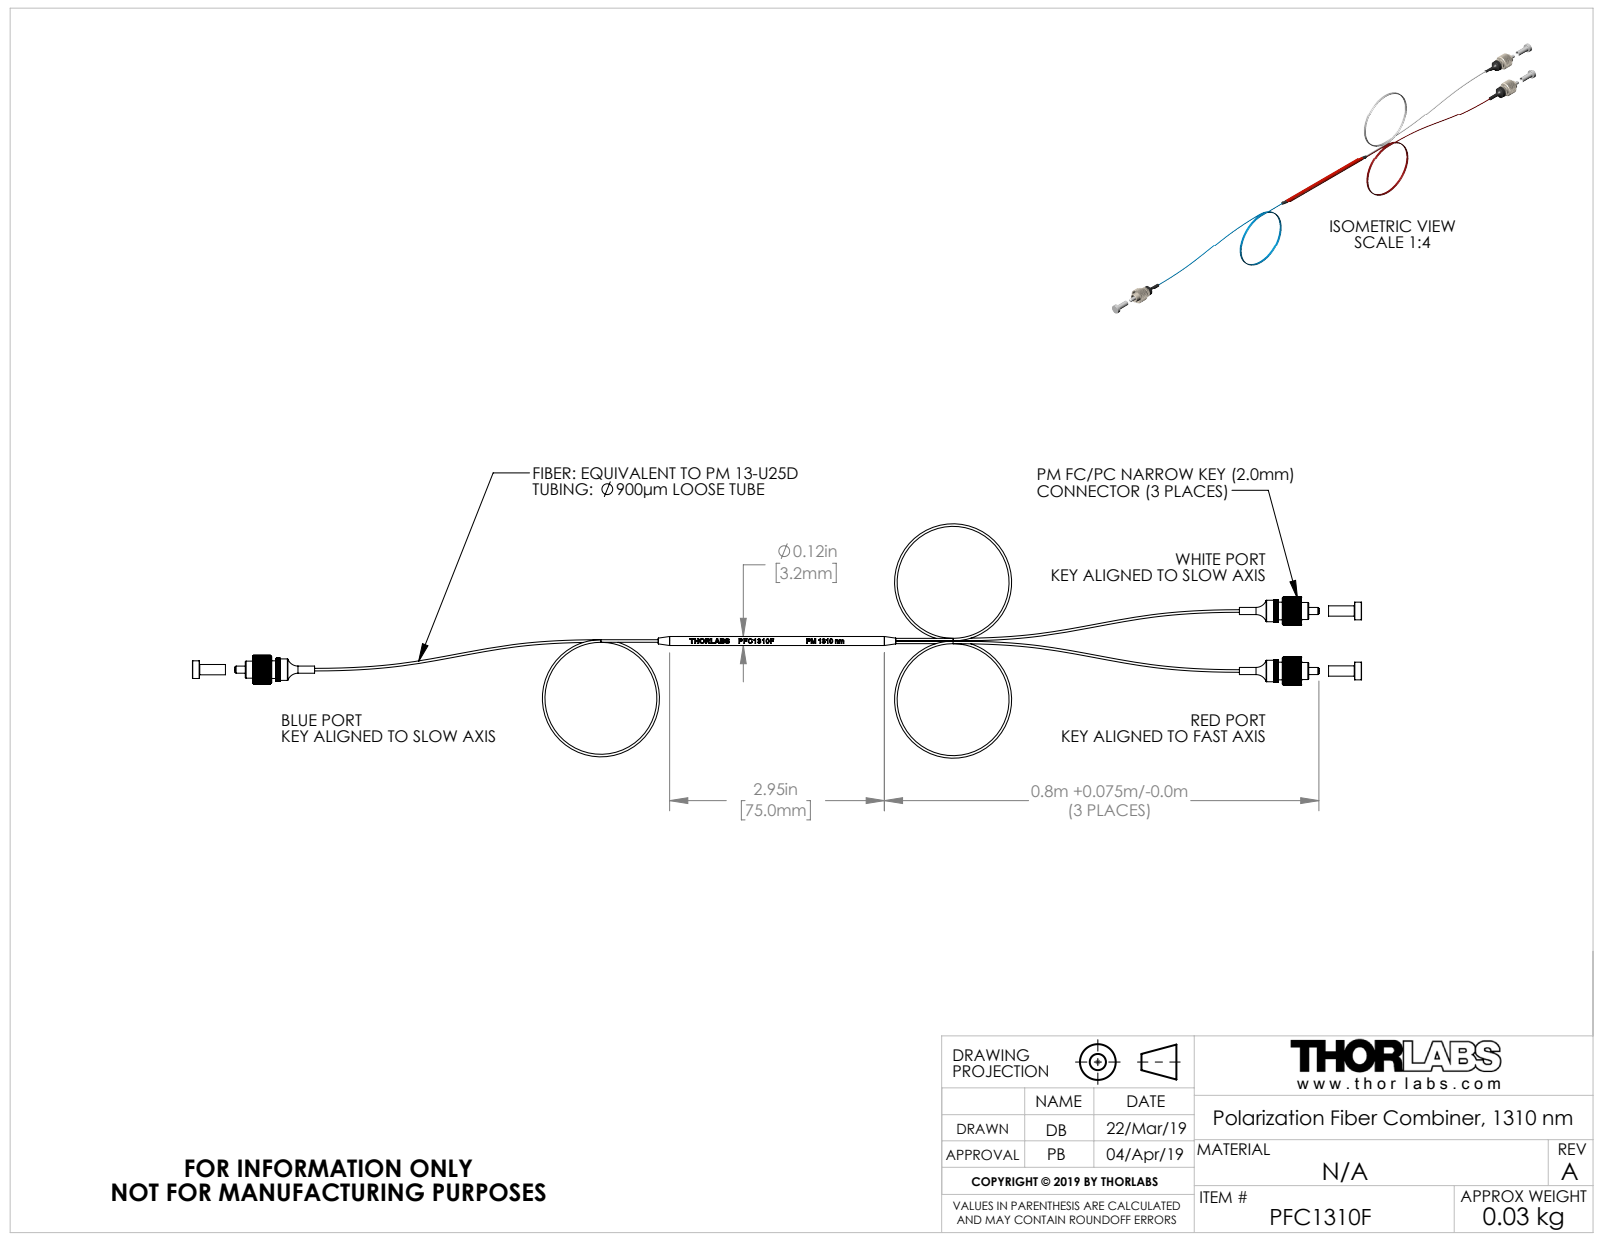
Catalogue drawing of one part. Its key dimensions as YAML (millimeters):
part_name: "DWG1751_48-2mm; PANDA 1310_60; DWG1631_75mm; DWG1528 (+8 more)"
step_written_by: "SolidWorks 2018 (CONFIG_CONTROL_DESIGN)"
units: millimeters
bodies: {solids: 32, faces: 2605, planar: 1271, cylindrical: 884, other: 450}
overall_size: [408.3, 81.85, 13.99]
volume: 3282
surface_area: 13603
round_holes:
  - {diameter: 0.5, count: 6}
  - {diameter: 0.9, count: 3}
  - {diameter: 0.95, count: 3}
  - {diameter: 1, count: 3}
  - {diameter: 2.5, count: 3}
  - {diameter: 2.8, count: 3}
  - {diameter: 3.36, count: 3}
  - {diameter: 4.38, count: 3}
  - {diameter: 4.4, count: 3}
  - {diameter: 5.08, count: 3}
  - {diameter: 5.55, count: 3}
  - {diameter: 6.1, count: 3}
round_bosses_or_shafts:
  - {diameter: 7.5, count: 3}
  - {diameter: 7.07, count: 3}
  - {diameter: 6.17, count: 3}
  - {diameter: 6.08, count: 3}
  - {diameter: 5.95, count: 3}
  - {diameter: 5.38, count: 3}
  - {diameter: 4.85, count: 3}
  - {diameter: 3.6, count: 3}
partial_cylinders:
  - {radius: 0.5, count: 6}
  - {radius: 0.75, count: 3}
  - {radius: 1.55, count: 3}
  - {radius: 2.26, count: 3}
  - {radius: 3.98, count: 3}
  - {radius: 5, count: 3}
  - {radius: 0.45, count: 2}
  - {radius: 1, count: 1}
face_to_face_distances: [6.86, 6.85, 2, 1.43, 4.97, 2.97, 349.97, 1.54, 3.43, 27.68]
hole_center_spacings: [10.2, 10.67, 11.13, 0.47, 0.48, 0.95, 4.03, 9.74]
